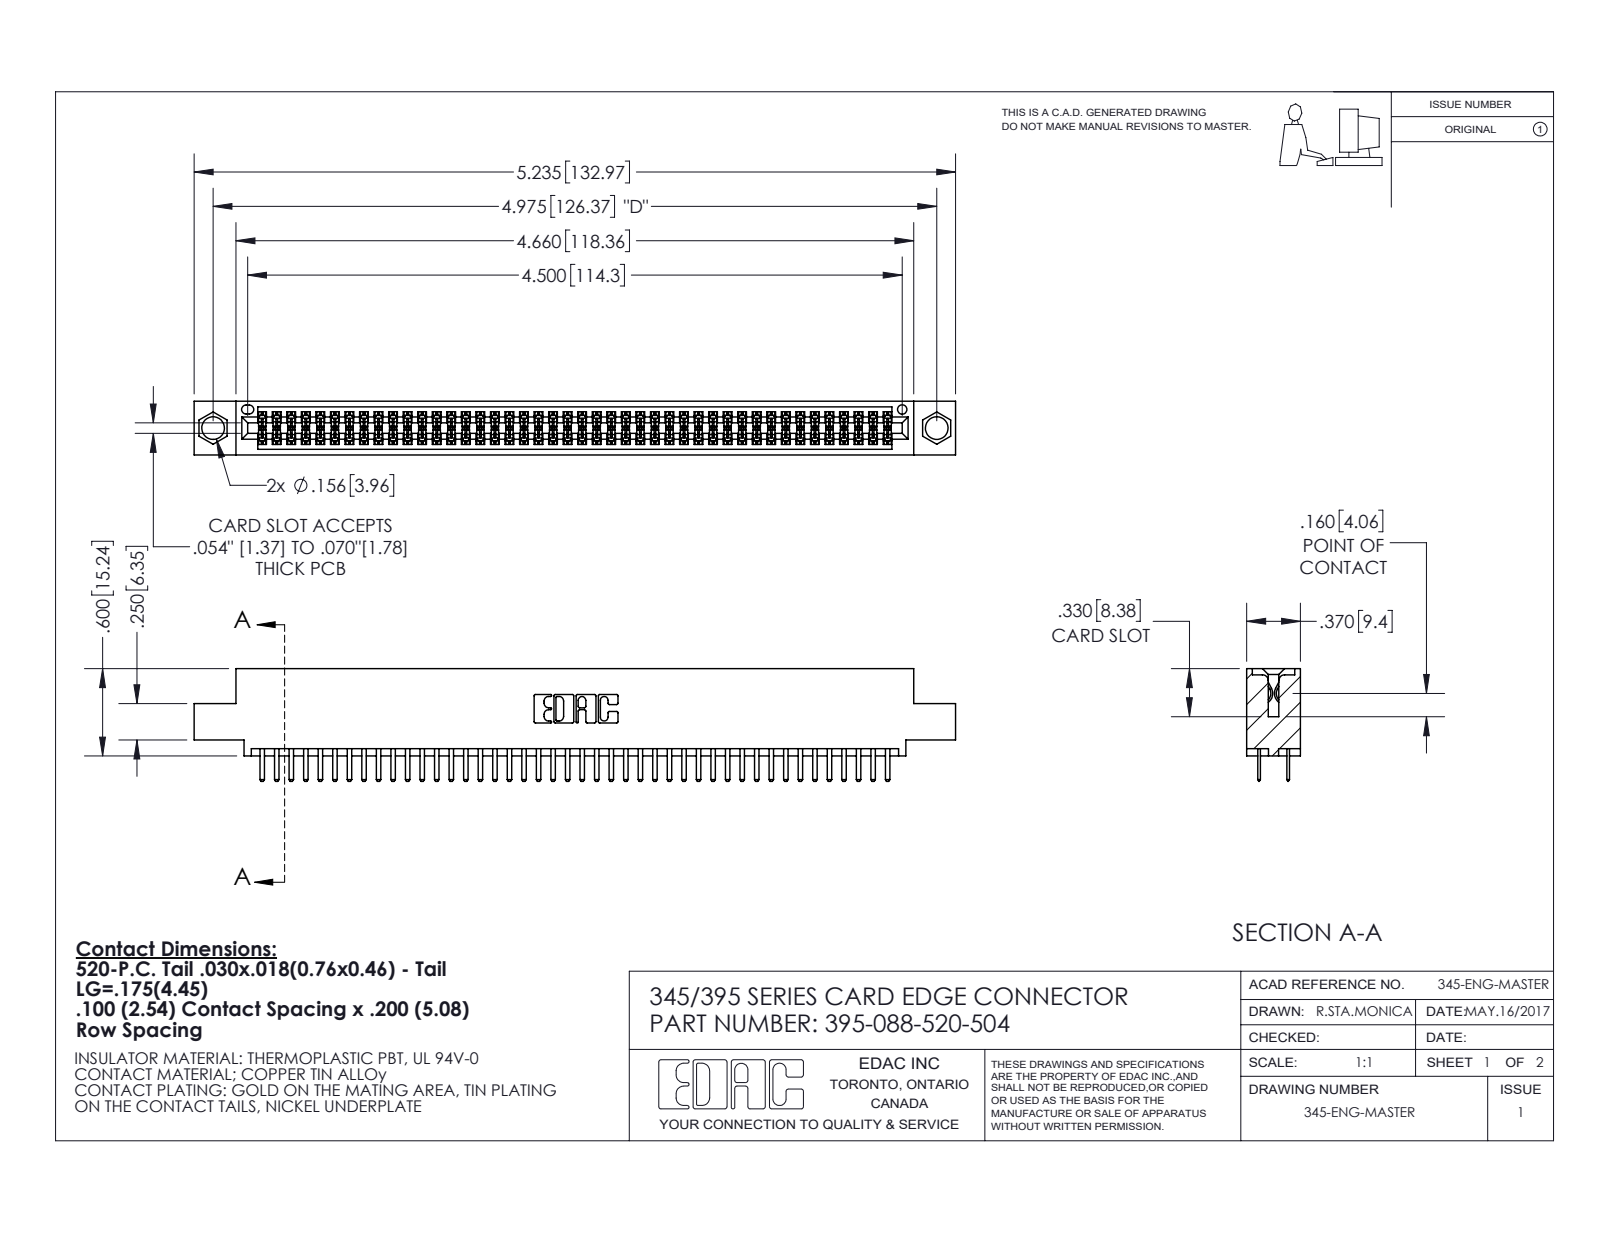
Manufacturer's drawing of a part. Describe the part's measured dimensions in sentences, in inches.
The part is named "395-088-520-504; 345-292-001_345-293-120; 345 Part_0.110 Offset - 0.156 Dia-TI". Its 3-D file was written by "SolidWorks 2020 (CONFIG_CONTROL_DESIGN)". It is 89 solids with 4896 faces: 3178 planar, 1718 cylindrical and 0 other. Overall it measures 5.235 by 0.775 by 0.37 inches. Its volume is 0.776 cubic inches and its surface area 28.98 square inches. Round holes: 2 of diameter 0.156, 1 of diameter 0.064. Partial cylindrical surfaces (rounded edges, fillets, slot ends): 176 of radius 0.006, 92 of radius 0.01, 22 of radius 0.01, 6 of radius 0.007, 6 of radius 0.031, 3 of radius 0.026, 2 of radius 0.014, 2 of radius 0.019. The main face-to-face distances are 0.072, 0.298, 0.2, 0.37, 0.098, 0.272, 0.025, 0.225, 0.022, 0.072. The hole center spacings are 0.27, 4.739, 4.975.
